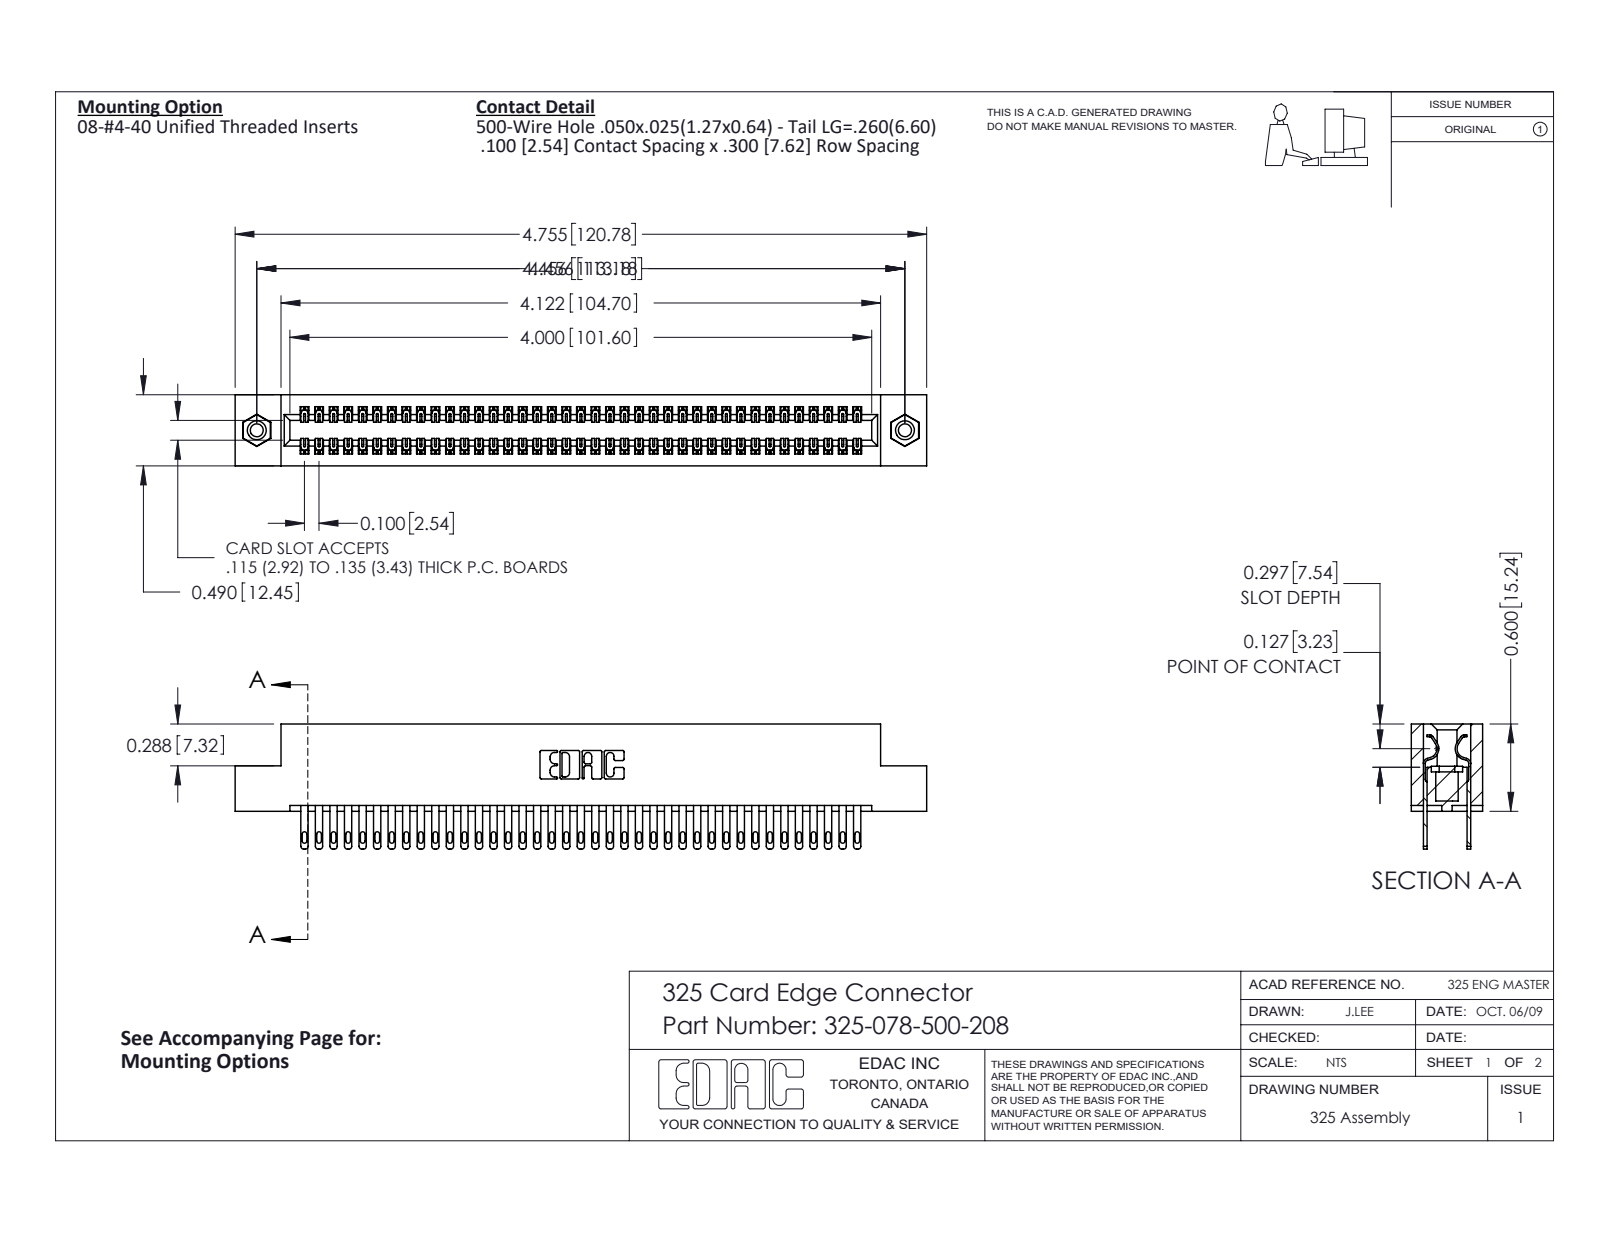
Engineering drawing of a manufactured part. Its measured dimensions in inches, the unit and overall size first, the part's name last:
Units: inches
Overall size (bounding box): 4.755 × 0.86 × 0.49
Round holes (diameter × count): ⌀0.089 ×2, ⌀0.125 ×2, ⌀0.16 ×2
Round bosses / shafts (diameter × count): ⌀0.155 ×2
Partial cylindrical surfaces — rounded edges, fillets, slot ends (radius × count): R0.006 ×117, R0.016 ×78, R0.02 ×78, R0.01 ×22, R0.007 ×6, R0.031 ×6, R0.026 ×3, R0.014 ×2
Main face-to-face distances: 0.083, 0.407, 0.3, 0.107, 0.383, 0.025, 0.49, 0.325, 0.275, 0.56
Hole centre spacings: 4.456
Volume: 0.964 in³ · Surface area: 30.81 in²
Bodies: 81 solids, 3918 faces (2442 planar, 1460 cylindrical, 16 other)
Part name (STEP PRODUCT): 325-078-500-208; 325-292-001_325-293-100; 325 Part_TI; 345-250-001_345-250-003-102
STEP written by: SolidWorks 2016 (CONFIG_CONTROL_DESIGN)
